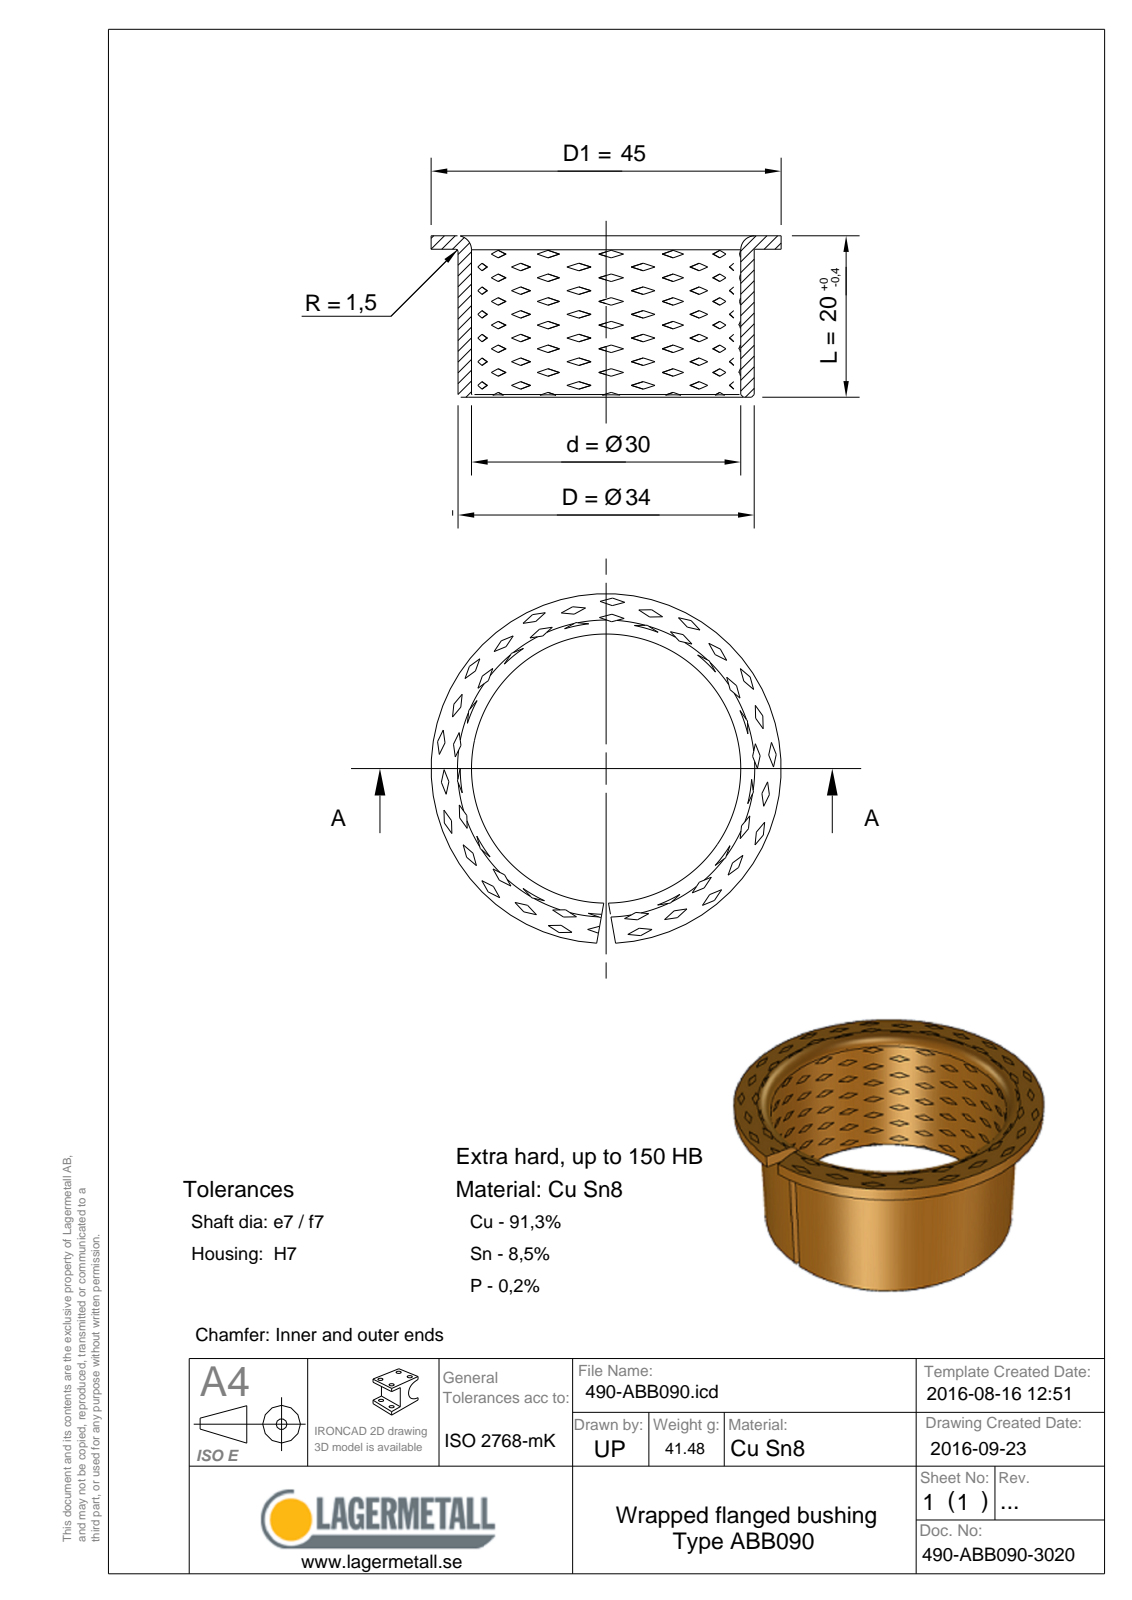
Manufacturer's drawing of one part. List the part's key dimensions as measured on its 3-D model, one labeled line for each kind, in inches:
STEP written by: Spatial InterOp 3D (CONFIG_CONTROL_DESIGN)
Units: inches
Bodies: 1 solid, 25 faces (5 planar, 8 cylindrical, 12 other)
Overall size (bounding box): 1.772 × 1.771 × 0.787
Volume: 0.313 in³ · Surface area: 8.767 in²
Round holes (diameter × count): ⌀1.181 ×1
Round bosses / shafts (diameter × count): ⌀1.772 ×1, ⌀1.339 ×1
Main face-to-face distances: 0.079, 0.709, 0.787
